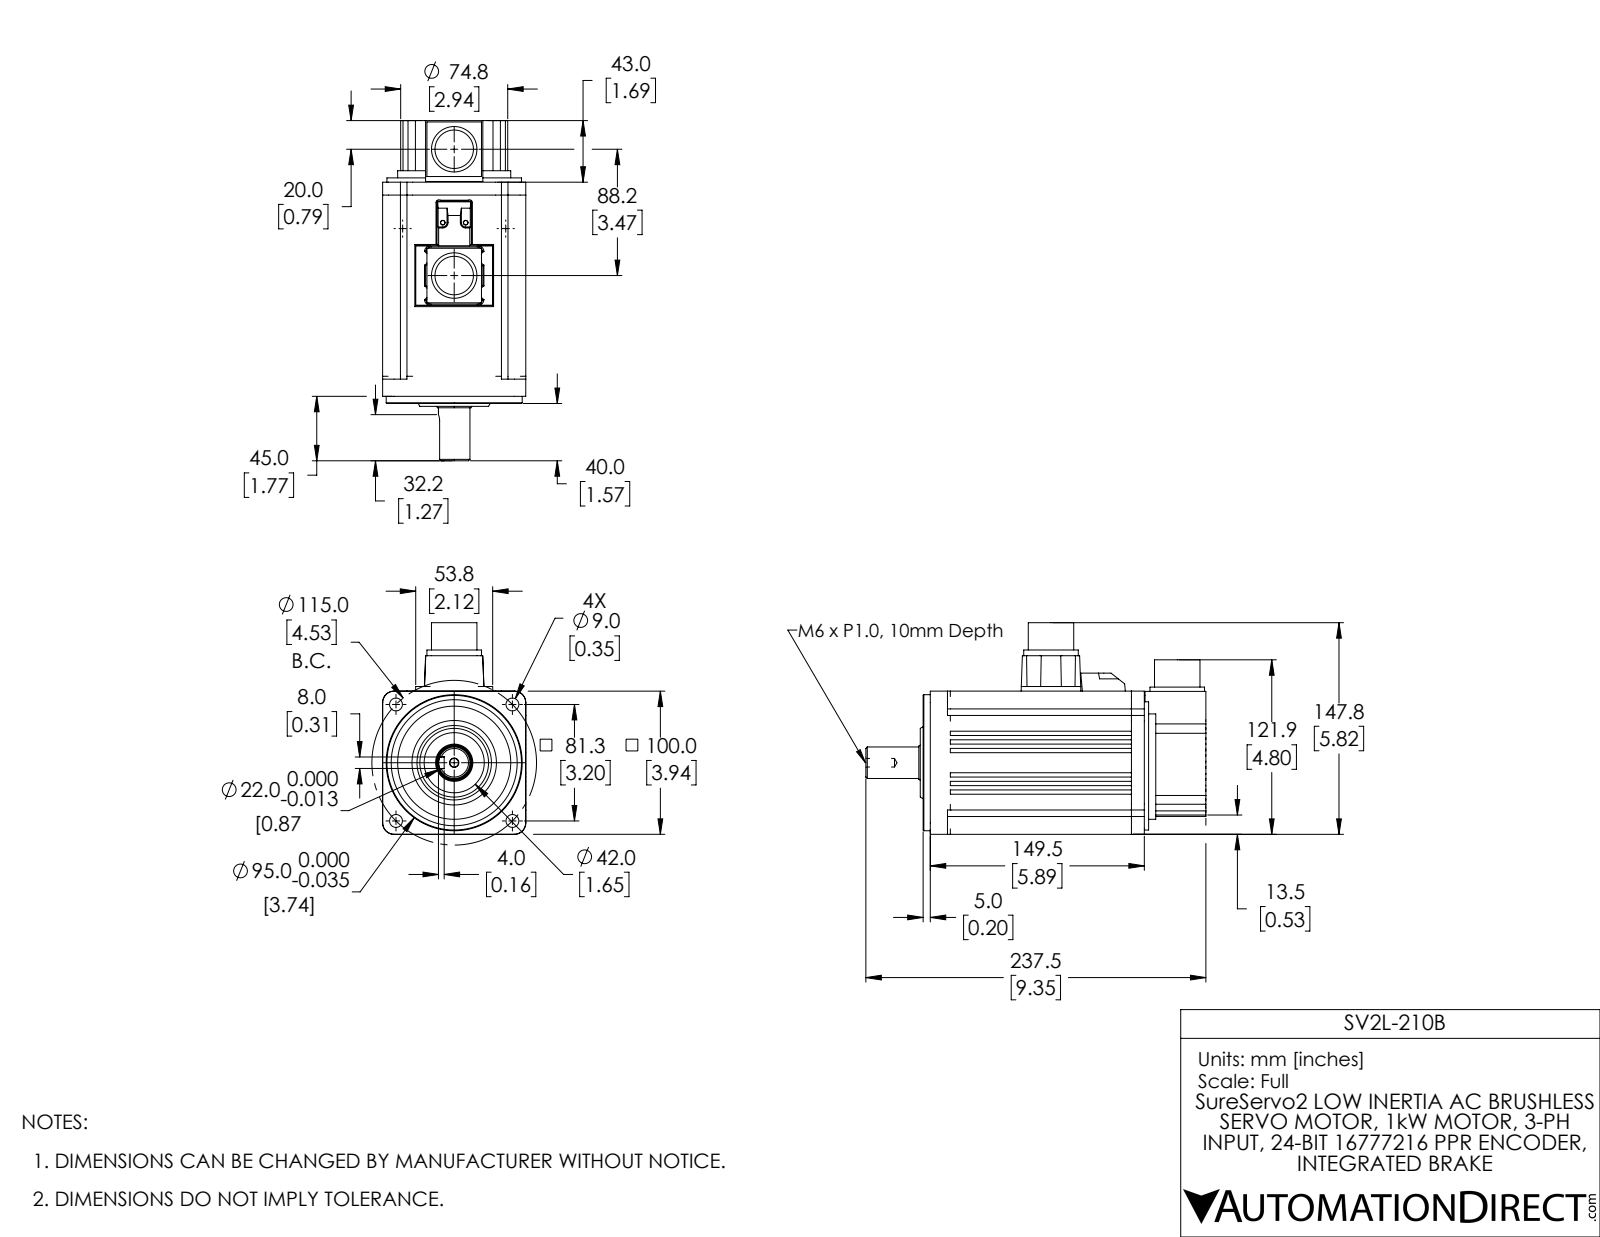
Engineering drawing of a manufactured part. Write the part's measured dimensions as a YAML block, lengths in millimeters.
part_name: "SV2L-210B"
step_written_by: "SolidWorks 2021 (AUTOMOTIVE_DESIGN)"
units: millimeters
bodies: {solids: 2, faces: 539, planar: 254, cylindrical: 235, other: 50}
overall_size: [237.5, 147.75, 100]
volume: 1632000
surface_area: 127297
round_holes:
  - {diameter: 9, count: 4}
  - {diameter: 3, count: 2}
  - {diameter: 3.3, count: 2}
  - {diameter: 26.88, count: 2}
  - {diameter: 6, count: 1}
  - {diameter: 26, count: 1}
  - {diameter: 42, count: 1}
  - {diameter: 79, count: 1}
  - {diameter: 88, count: 1}
round_bosses_or_shafts:
  - {diameter: 31.75, count: 2}
  - {diameter: 95, count: 1}
  - {diameter: 94, count: 1}
  - {diameter: 79, count: 1}
  - {diameter: 59, count: 1}
  - {diameter: 24.5, count: 1}
  - {diameter: 22, count: 1}
partial_cylinders:
  - {radius: 1, count: 44}
  - {radius: 2, count: 21}
  - {radius: 4, count: 21}
  - {radius: 0.2, count: 8}
  - {radius: 2, count: 2}
  - {radius: 35.5, count: 1}
  - {radius: 47.75, count: 1}
  - {radius: 49.5, count: 1}
face_to_face_distances: [17, 3, 100, 83, 6, 66, 11, 35, 40, 38]
hole_center_spacings: [57.5, 81.32, 37.79, 51.87, 115, 16, 88.18]
